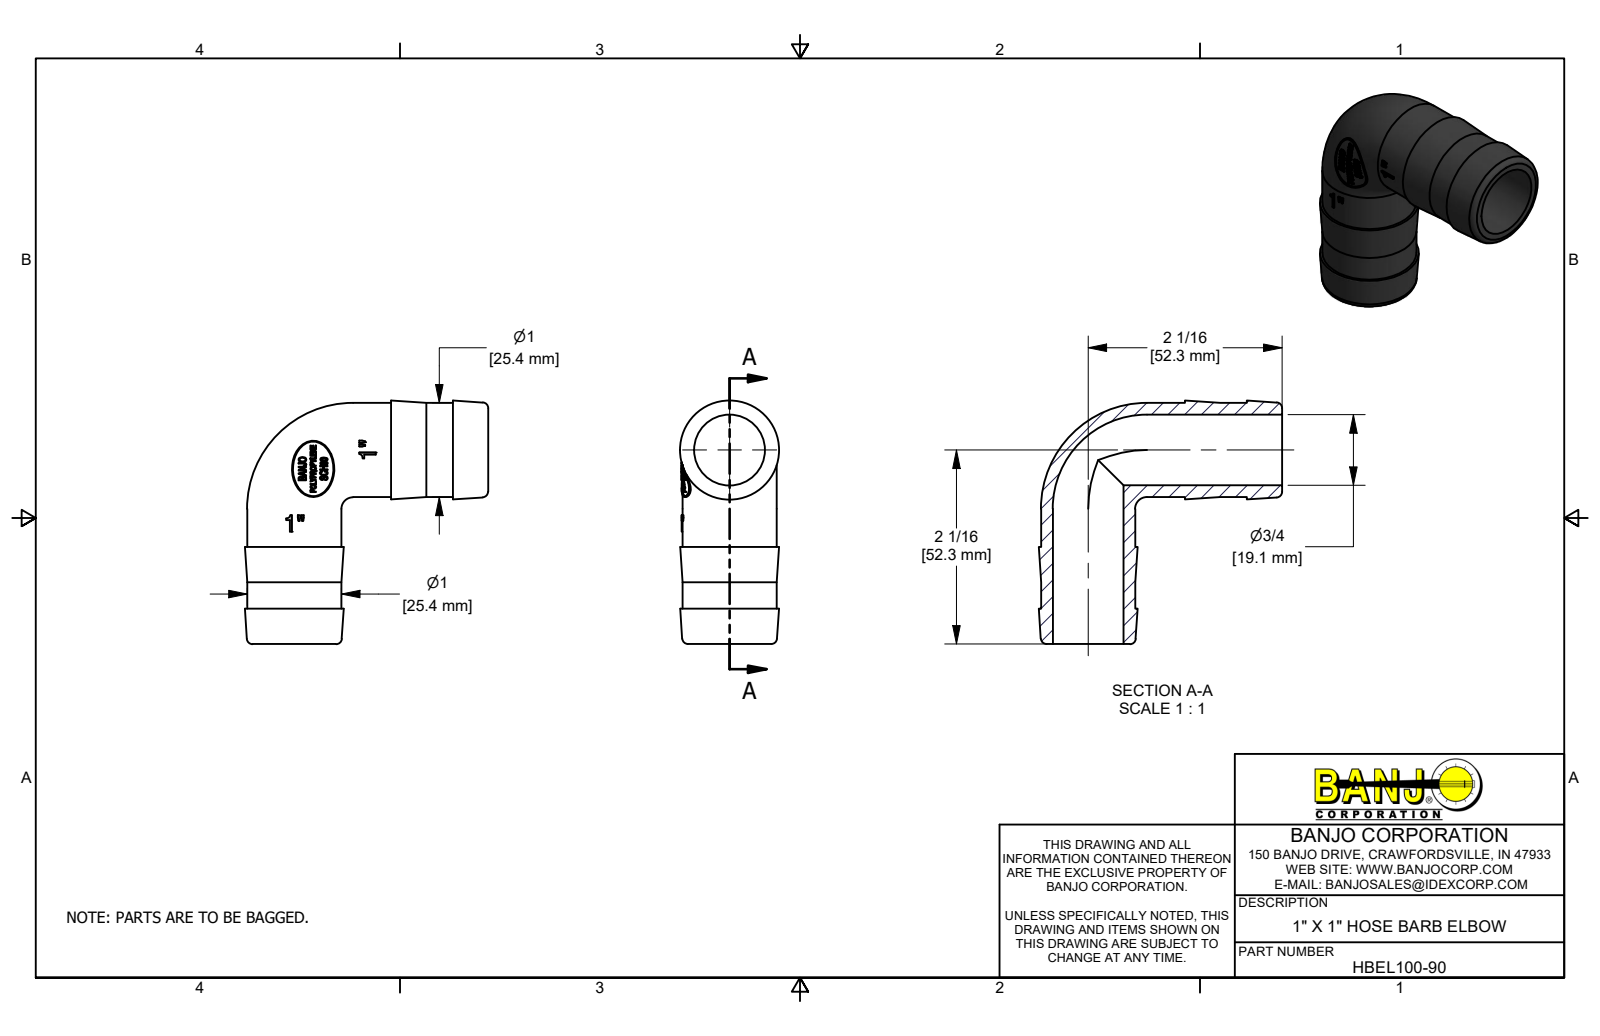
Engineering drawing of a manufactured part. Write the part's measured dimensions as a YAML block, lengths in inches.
part_name: "HBEL100-90; HBEL100-90U"
step_written_by: "Autodesk Inventor 2019 (AUTOMOTIVE_DESIGN)"
units: inches
bodies: {solids: 1, faces: 402, planar: 192, cylindrical: 12, other: 198}
overall_size: [2.585, 2.585, 1.05]
volume: 1.398
surface_area: 22.33
round_holes:
  - {diameter: 0.75, count: 2}
round_bosses_or_shafts:
  - {diameter: 1, count: 2}
partial_cylinders:
  - {radius: 0.51, count: 2}
face_to_face_distances: [1.031, 0.375, 0.656, 2.048, 1.674, 1.017, 0.857, 1.514, 1.889, 0.028]
